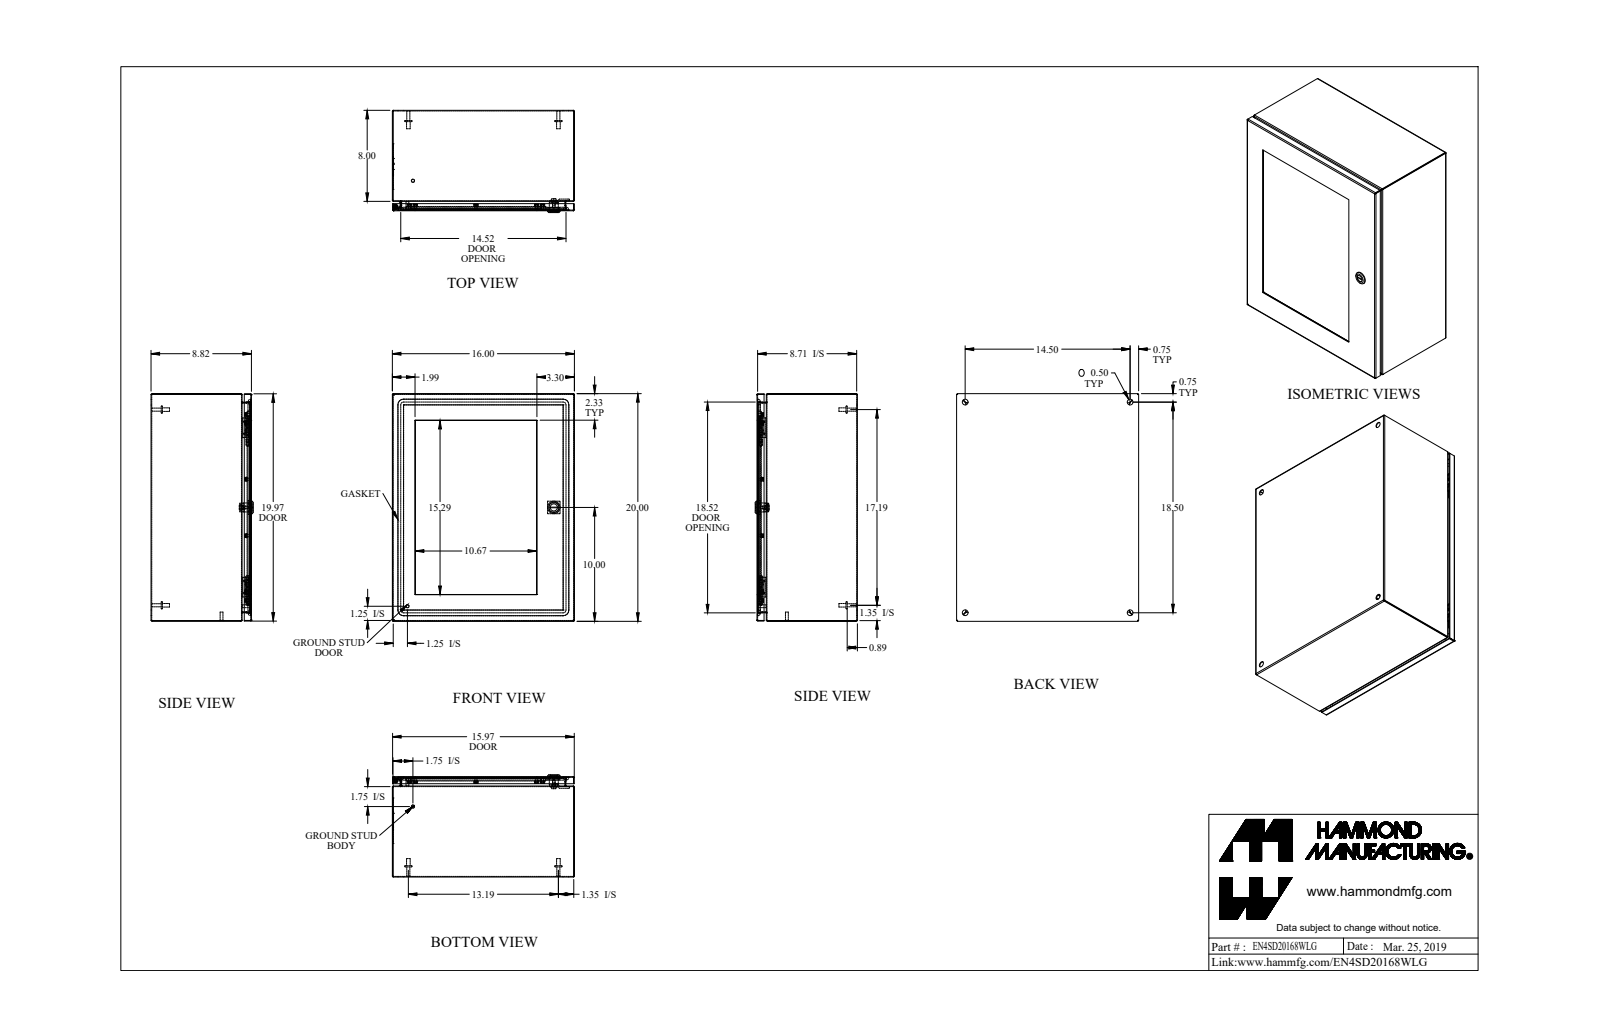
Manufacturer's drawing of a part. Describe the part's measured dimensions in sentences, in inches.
The part is named "EN4SD20168WLG_Default". Its 3-D file was written by "SolidWorks 2019 (CONFIG_CONTROL_DESIGN)". It is 58 solids with 1197 faces: 594 planar, 369 cylindrical and 234 other. Overall it measures 20 by 16 by 8.982 inches. Its volume is 124.5 cubic inches and its surface area 3 090 square inches. Round holes: 14 of diameter 0.13, 14 of diameter 0.25, 4 of diameter 0.5, 1 of diameter 0.172, 1 of diameter 0.232, 1 of diameter 0.24, 1 of diameter 0.242, 1 of diameter 0.625, 1 of diameter 0.785. Round bosses or shafts: 15 of diameter 0.226, 14 of diameter 0.368, 14 of diameter 0.164, 4 of diameter 0.625, 4 of diameter 0.313, 4 of diameter 0.27, 2 of diameter 0.281, 2 of diameter 0.25. Partial cylindrical surfaces (rounded edges, fillets, slot ends): 21 of radius 0.029, 21 of radius 0.086, 16 of radius 0.25, 10 of radius 0.125, 8 of radius 19, 4 of radius 0.006, 4 of radius 0.016, 4 of radius 0.062. The main face-to-face distances are 0.057, 8.765, 8.708, 15.943, 19.943, 0.25, 8.458, 8.515, 15.886, 16. The hole center spacings are 4.958, 15.612, 15.614, 5.335, 9.917, 12.551, 12.714, 12.716.
